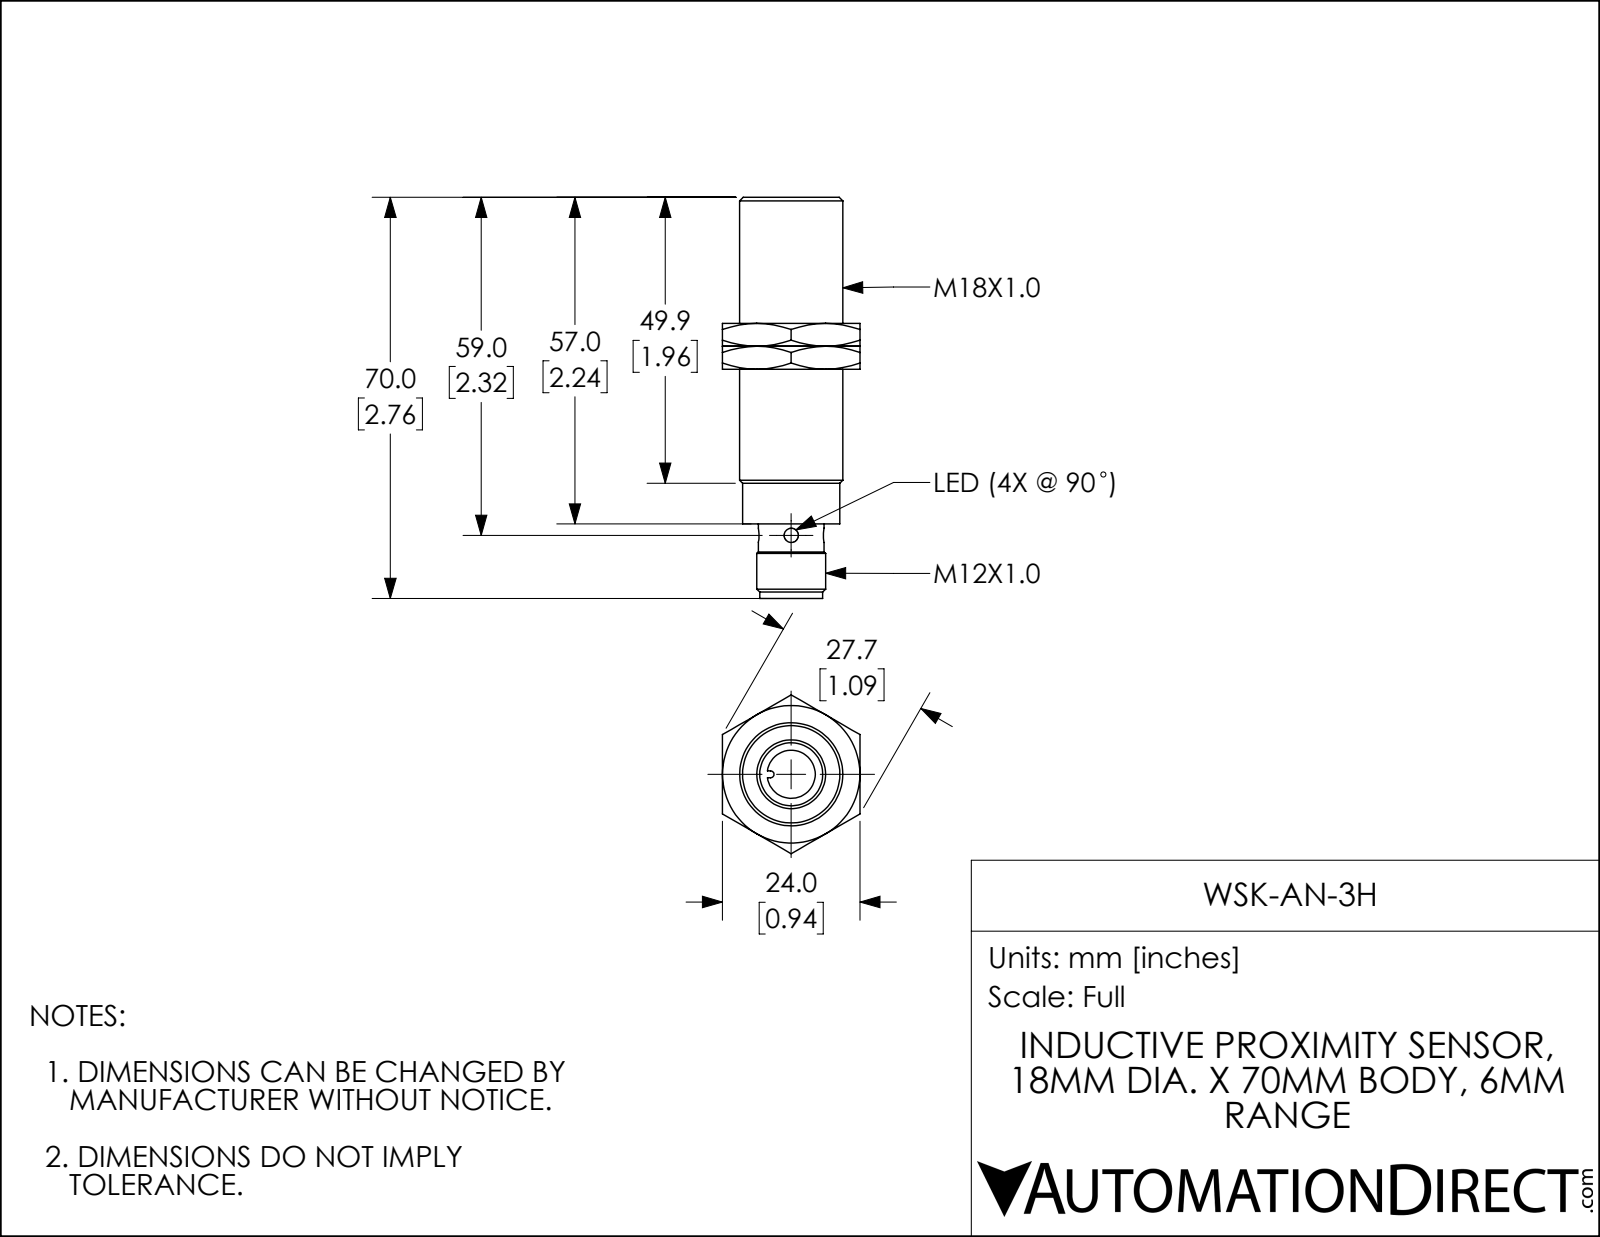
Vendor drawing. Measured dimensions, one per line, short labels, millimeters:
name: WSK-AN-3H
written by: SolidWorks 2017 (AUTOMOTIVE_DESIGN)
unit: mm
bodies: 3 solids, 71 faces (22 planar, 13 cylindrical, 36 other)
size: 70 × 27.7 × 24
volume: 17 290 mm³; area: 6 471 mm²
holes: 1× ⌀8.4, 1× ⌀16.9
bosses: 1× ⌀18, 1× ⌀17, 1× ⌀12, 1× ⌀11.5, 1× ⌀11
rounds: 4× R5.7, 1× R0.6
face distances: 4, 24, 26, 22, 8, 30, 27, 31, 35, 57
